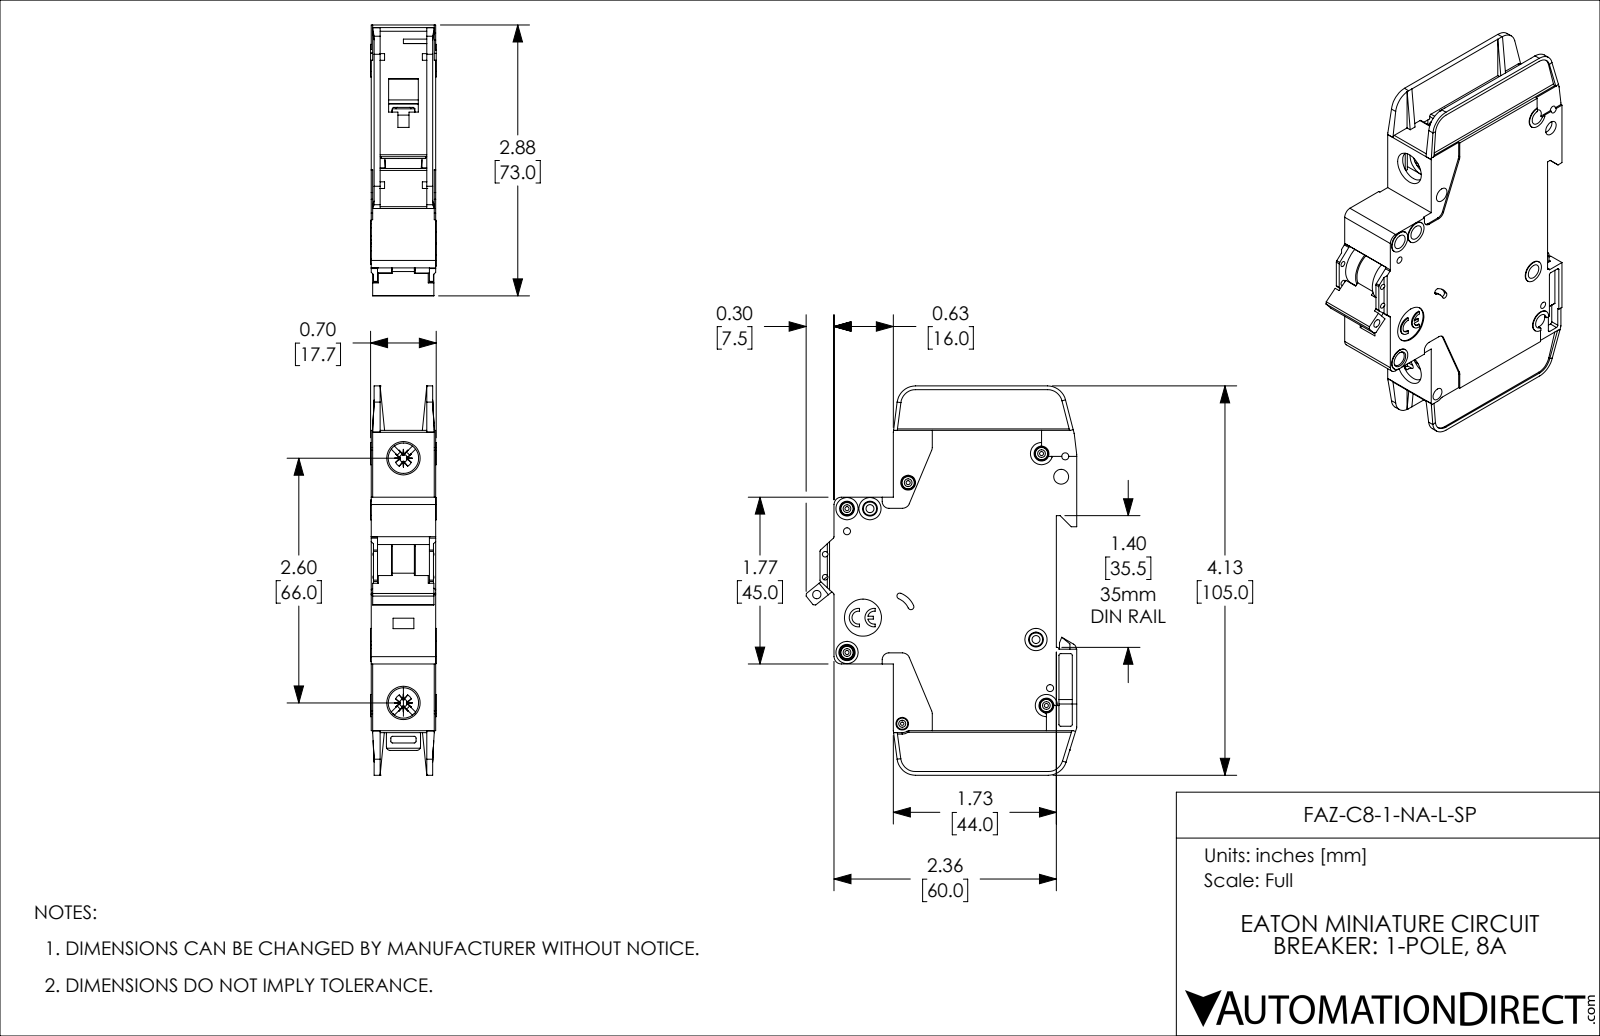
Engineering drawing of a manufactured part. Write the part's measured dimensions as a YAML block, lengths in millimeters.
part_name: "FAZ-C8-1-NA-L-SP"
step_written_by: "SolidWorks 2019 (AUTOMOTIVE_DESIGN)"
units: millimeters
bodies: {solids: 1, faces: 1127, planar: 671, cylindrical: 357, other: 99}
overall_size: [105, 73.1, 17.7]
volume: 76720
surface_area: 26460
round_holes:
  - {diameter: 4, count: 8}
  - {diameter: 1.1, count: 5}
  - {diameter: 1.9, count: 4}
  - {diameter: 1.5, count: 2}
  - {diameter: 2.2, count: 2}
  - {diameter: 8.2, count: 2}
  - {diameter: 0.9, count: 1}
  - {diameter: 2.3, count: 1}
  - {diameter: 2.5, count: 1}
  - {diameter: 3.4, count: 1}
  - {diameter: 10, count: 1}
round_bosses_or_shafts:
  - {diameter: 3.3, count: 5}
  - {diameter: 6, count: 4}
  - {diameter: 3, count: 2}
  - {diameter: 2.5, count: 1}
partial_cylinders:
  - {radius: 0.5, count: 42}
  - {radius: 0.4, count: 10}
  - {radius: 1, count: 10}
  - {radius: 2, count: 8}
  - {radius: 5, count: 5}
  - {radius: 0.2, count: 4}
  - {radius: 0.7, count: 4}
  - {radius: 1.1, count: 4}
face_to_face_distances: [1.2, 17.4, 15, 16.2, 2.4, 13.8, 0.4, 0.8, 12.6, 14.6]
hole_center_spacings: [6.2, 13.6, 22.1, 4.8, 5.1, 5.2, 5.6, 6.1]
